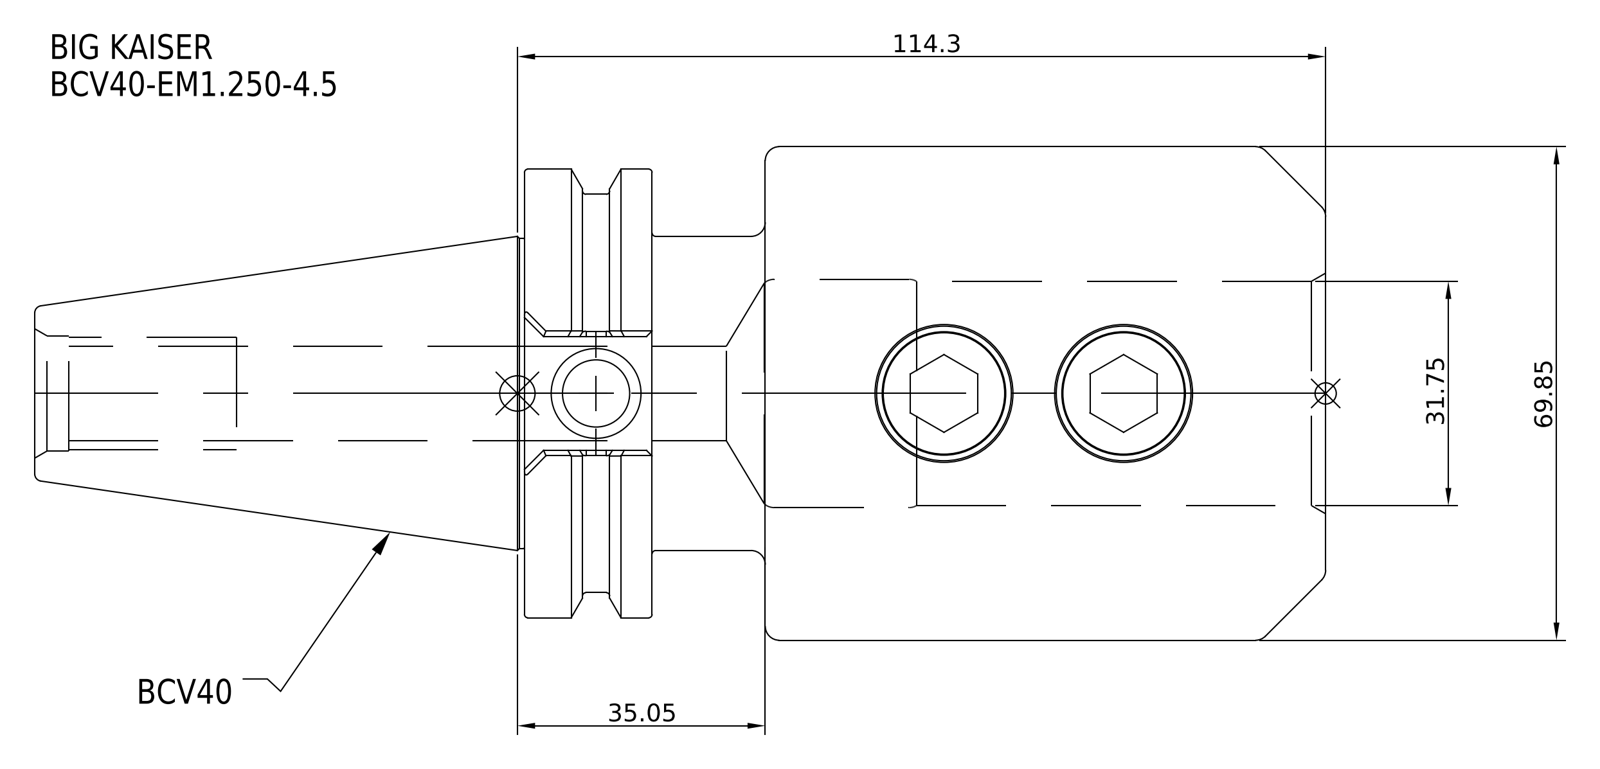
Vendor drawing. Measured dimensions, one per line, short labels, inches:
name: BCV40-EM1_250-4_5
written by: SolidWorks 2021 (CONFIG_CONTROL_DESIGN)
unit: in
bodies: 1 solid, 30 faces (8 planar, 14 cylindrical, 8 other)
size: 7.187 × 2.752 × 2.752
volume: 23.11 in³; area: 74.54 in²
holes: 1× ⌀1.25
bosses: 1× ⌀2.752, 1× ⌀2.5, 1× ⌀2.219, 1× ⌀1.75
face distances: 1.341, 0.63, 0.711, 3.12, 3.75, 4.461, 7.187, 4.067, 3.437, 2.726
